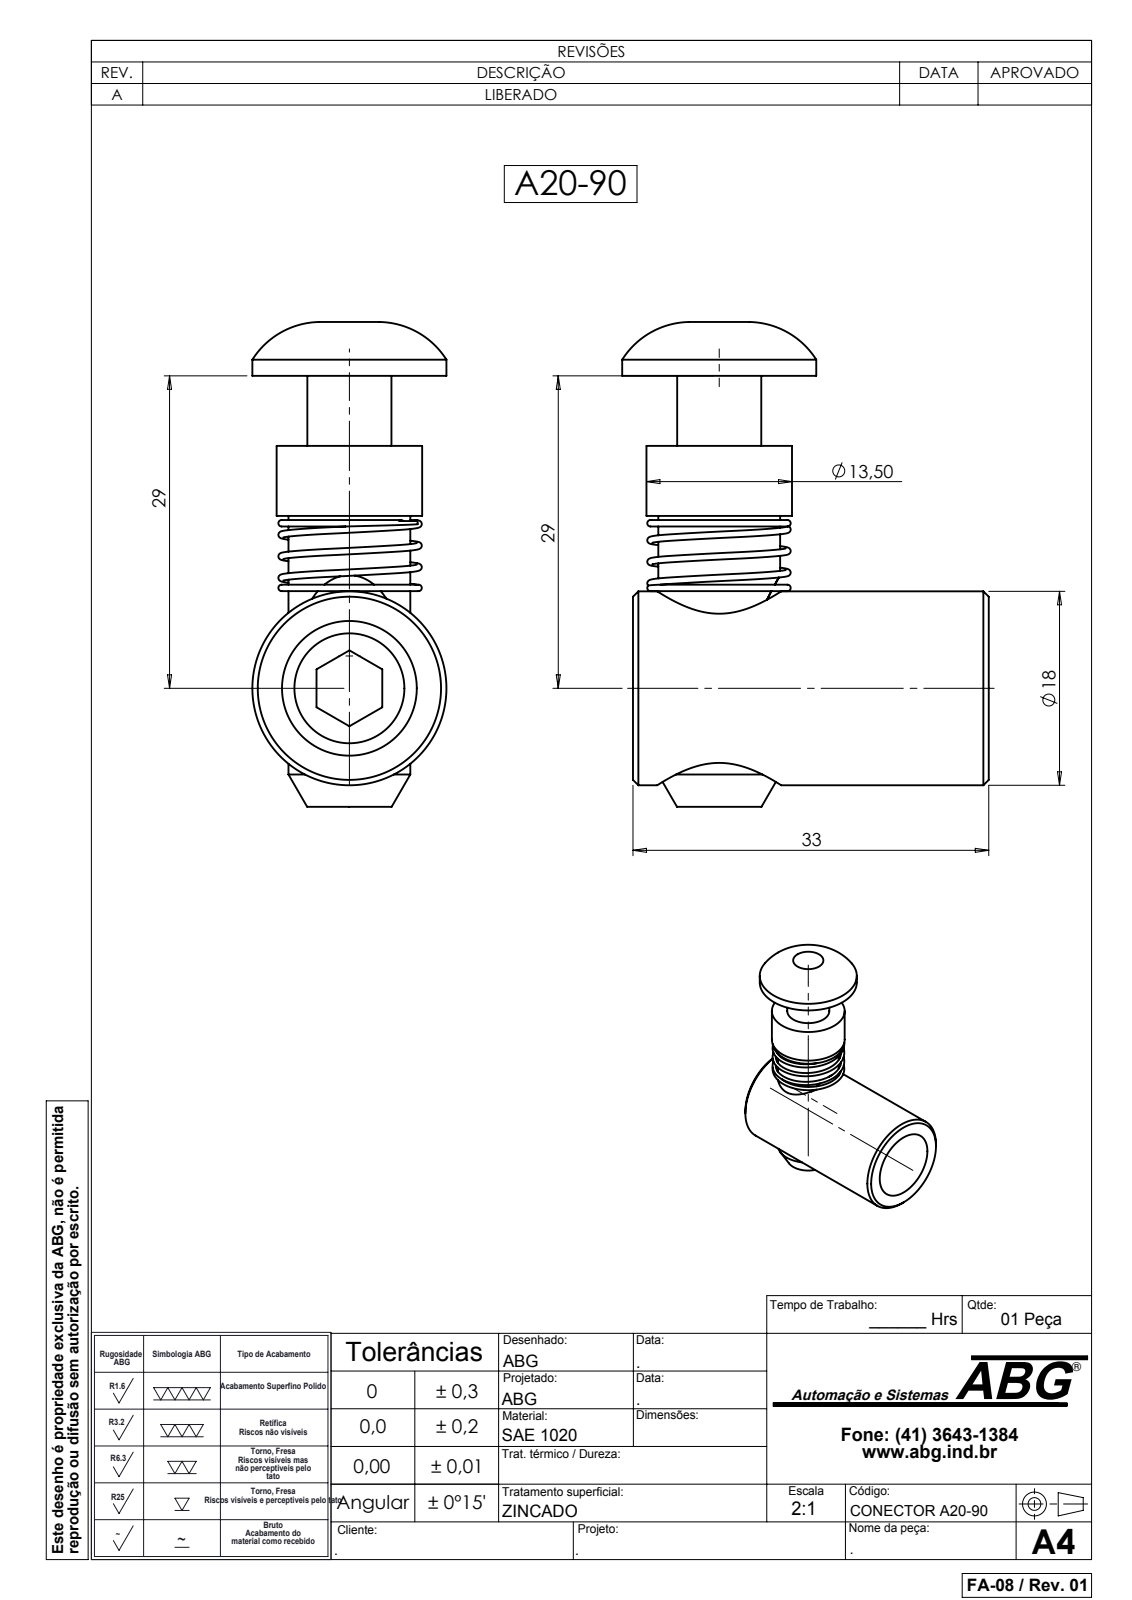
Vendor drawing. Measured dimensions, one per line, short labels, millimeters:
name: A20-90; BUCHA 220-10; PARAFUSO 125-80; MOLA 225-10 (+1 more)
written by: SolidWorks 2007 (CONFIG_CONTROL_DESIGN)
unit: mm
bodies: 4 solids, 63 faces (21 planar, 18 cylindrical, 24 other)
size: 45 × 34 × 18
volume: 9 960 mm³; area: 6 456 mm²
holes: 1× ⌀10.2, 1× ⌀11.5, 1× ⌀12.5
bosses: 2× ⌀18, 1× ⌀13.5, 1× ⌀12, 1× ⌀11.3, 1× ⌀7.8
face distances: 6.5, 33, 21.94, 11.06, 6.1, 33.5, 40, 27, 13, 23
